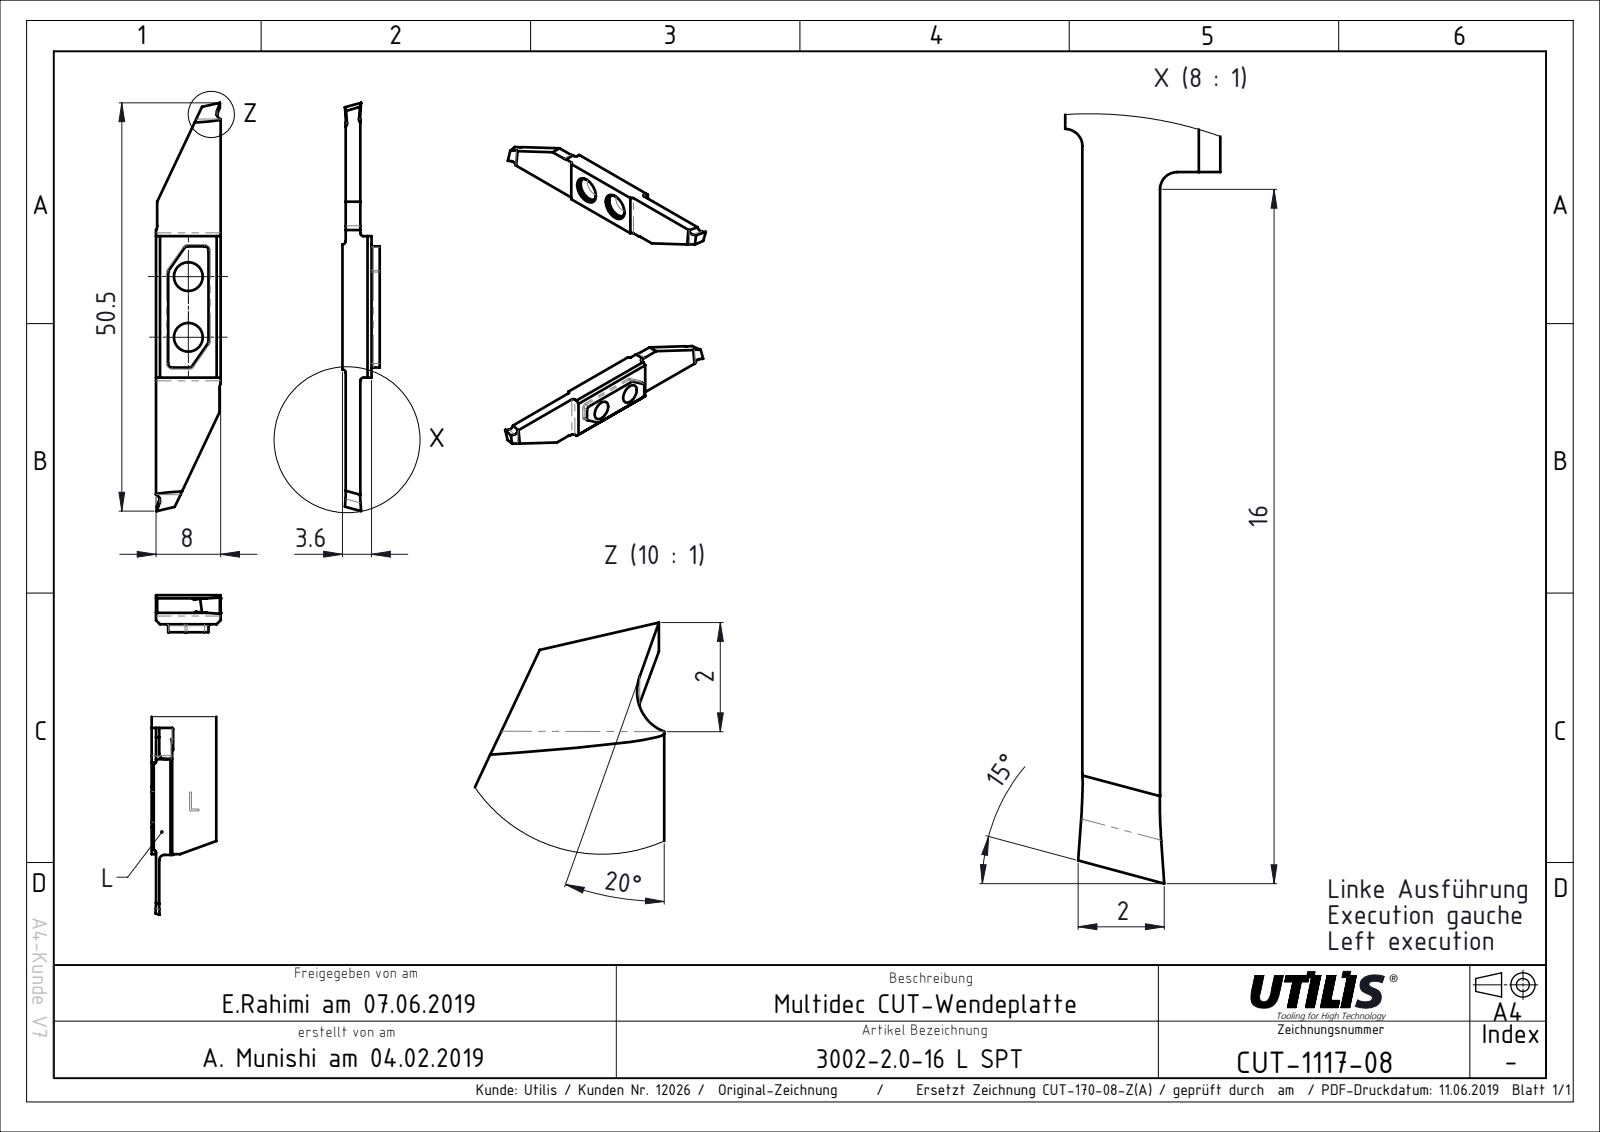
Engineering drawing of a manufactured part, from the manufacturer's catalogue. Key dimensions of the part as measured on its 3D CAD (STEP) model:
Part name (STEP PRODUCT): CUT-1117; ASME Y14.5
STEP written by: FormatWorks Professional (AP242_MANAGED_MODEL_BASED_3D_ENGINEERING_MIM_LF)
Units: millimetres
Bodies: 1 solid, 34 faces (24 planar, 10 cylindrical, 0 other)
Overall size (bounding box): 50.5 × 8 × 3.6
Volume: 759 mm³ · Surface area: 964 mm²
Round holes (diameter × count): ⌀3.55 ×2
Partial cylindrical surfaces — rounded edges, fillets, slot ends (radius × count): R0.4 ×4, R1 ×2
Main face-to-face distances: 1.78, 0.41, 2.19, 3.6, 3.19, 1.41, 8, 18.09, 7.85, 17.5
Hole centre spacings: 7.5
